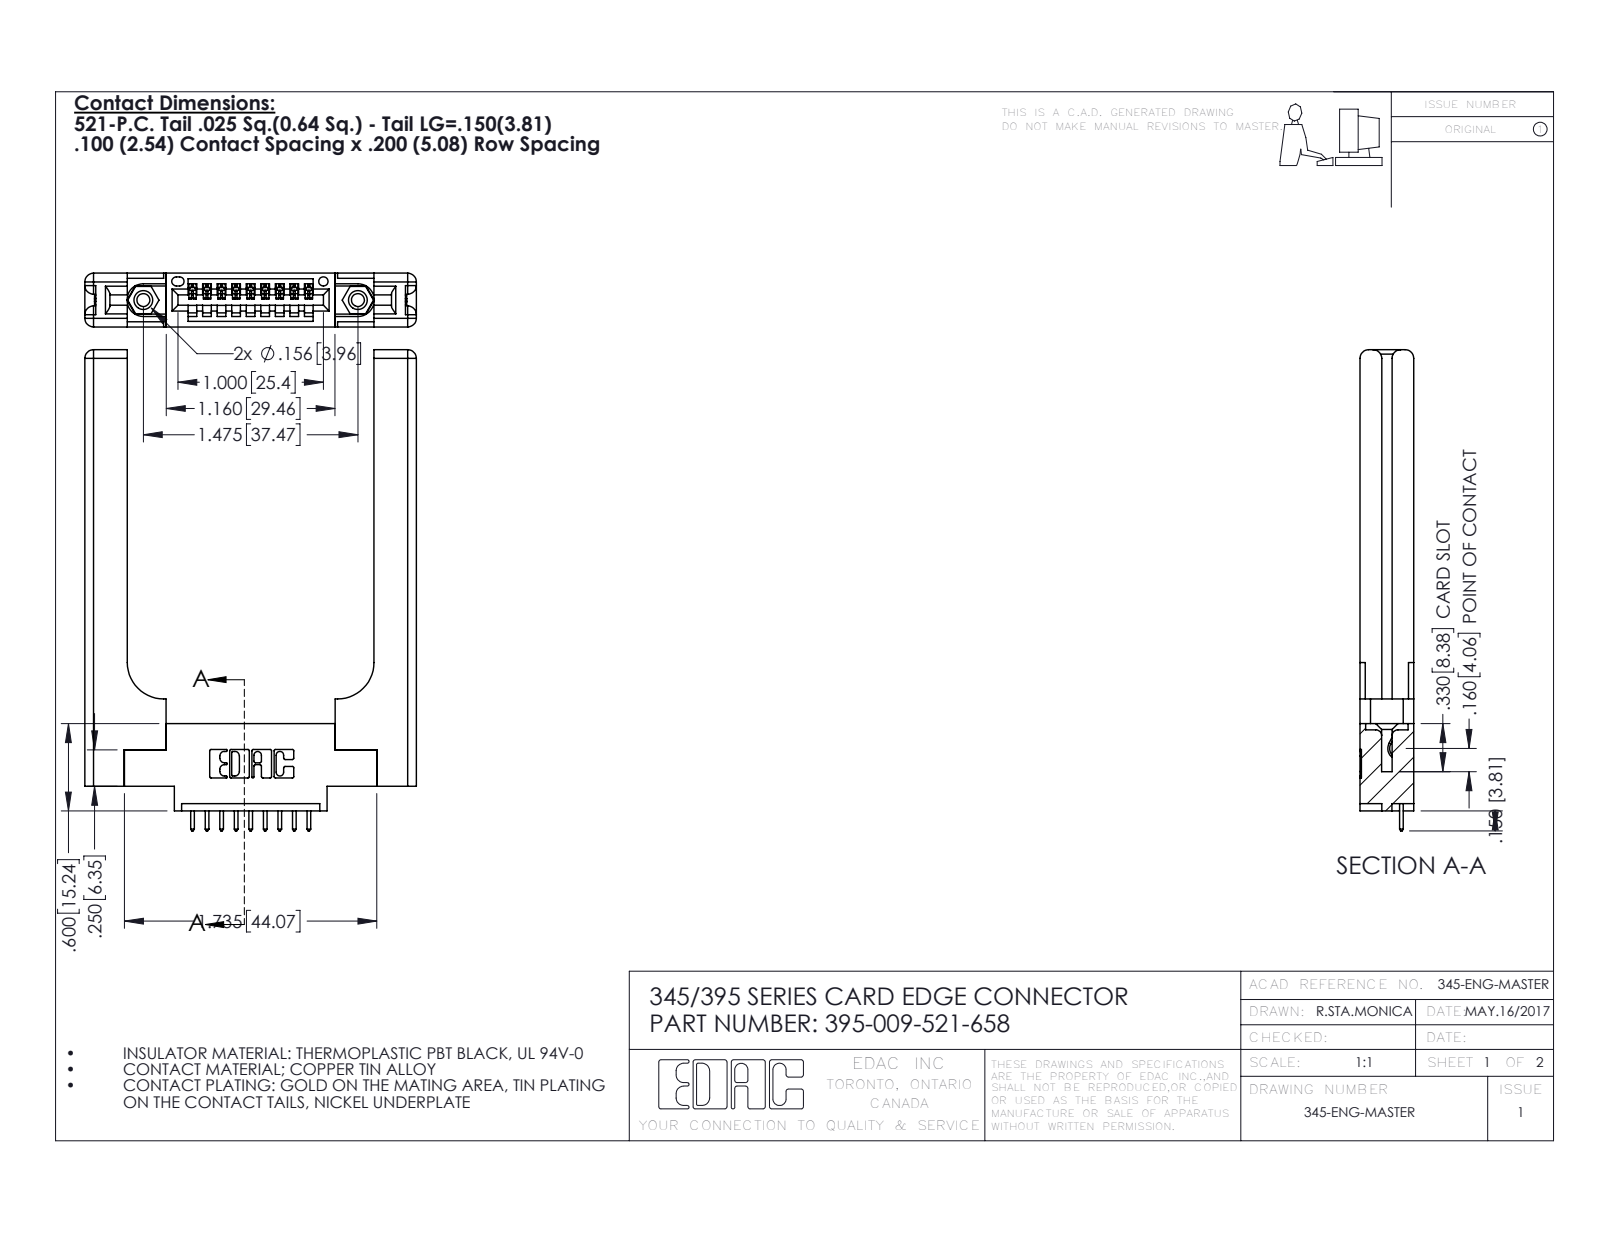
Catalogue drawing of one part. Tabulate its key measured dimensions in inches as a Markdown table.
| quantity | value |
| --- | --- |
| part name | 345-220-058_345-220-058; 345 Part_0.170 Offset - 0.156 Dia-TH; 395-009-521-658; 345-292-001_345-293-121 (+1 more) |
| STEP written by | SolidWorks 2016 (CONFIG_CONTROL_DESIGN) |
| units | inches |
| bodies | 14 solids, 908 faces (592 planar, 256 cylindrical, 60 other) |
| overall size | 3.307 × 2.279 × 0.37 |
| volume | 0.83 in³ |
| surface area | 18.05 in² |
| round holes (diameter × count) | 0.089 × 2, 0.125 × 2, 0.156 × 2, 0.064 × 1 |
| round bosses / shafts (diameter × count) | 0.155 × 2 |
| partial cylindrical surfaces (radius × count) | 0.01 × 22, 0.006 × 18, 0.01 × 18, 0.06 × 16, 0.007 × 6, 0.031 × 6, 0.026 × 3, 0.03 × 2 |
| main face-to-face distances | 0.37, 0.15, 0.22, 0.072, 0.077, 0.148, 0.298, 1.696, 0.071, 0.12 |
| hole center spacings | 0.27, 1.244, 1.475 |
